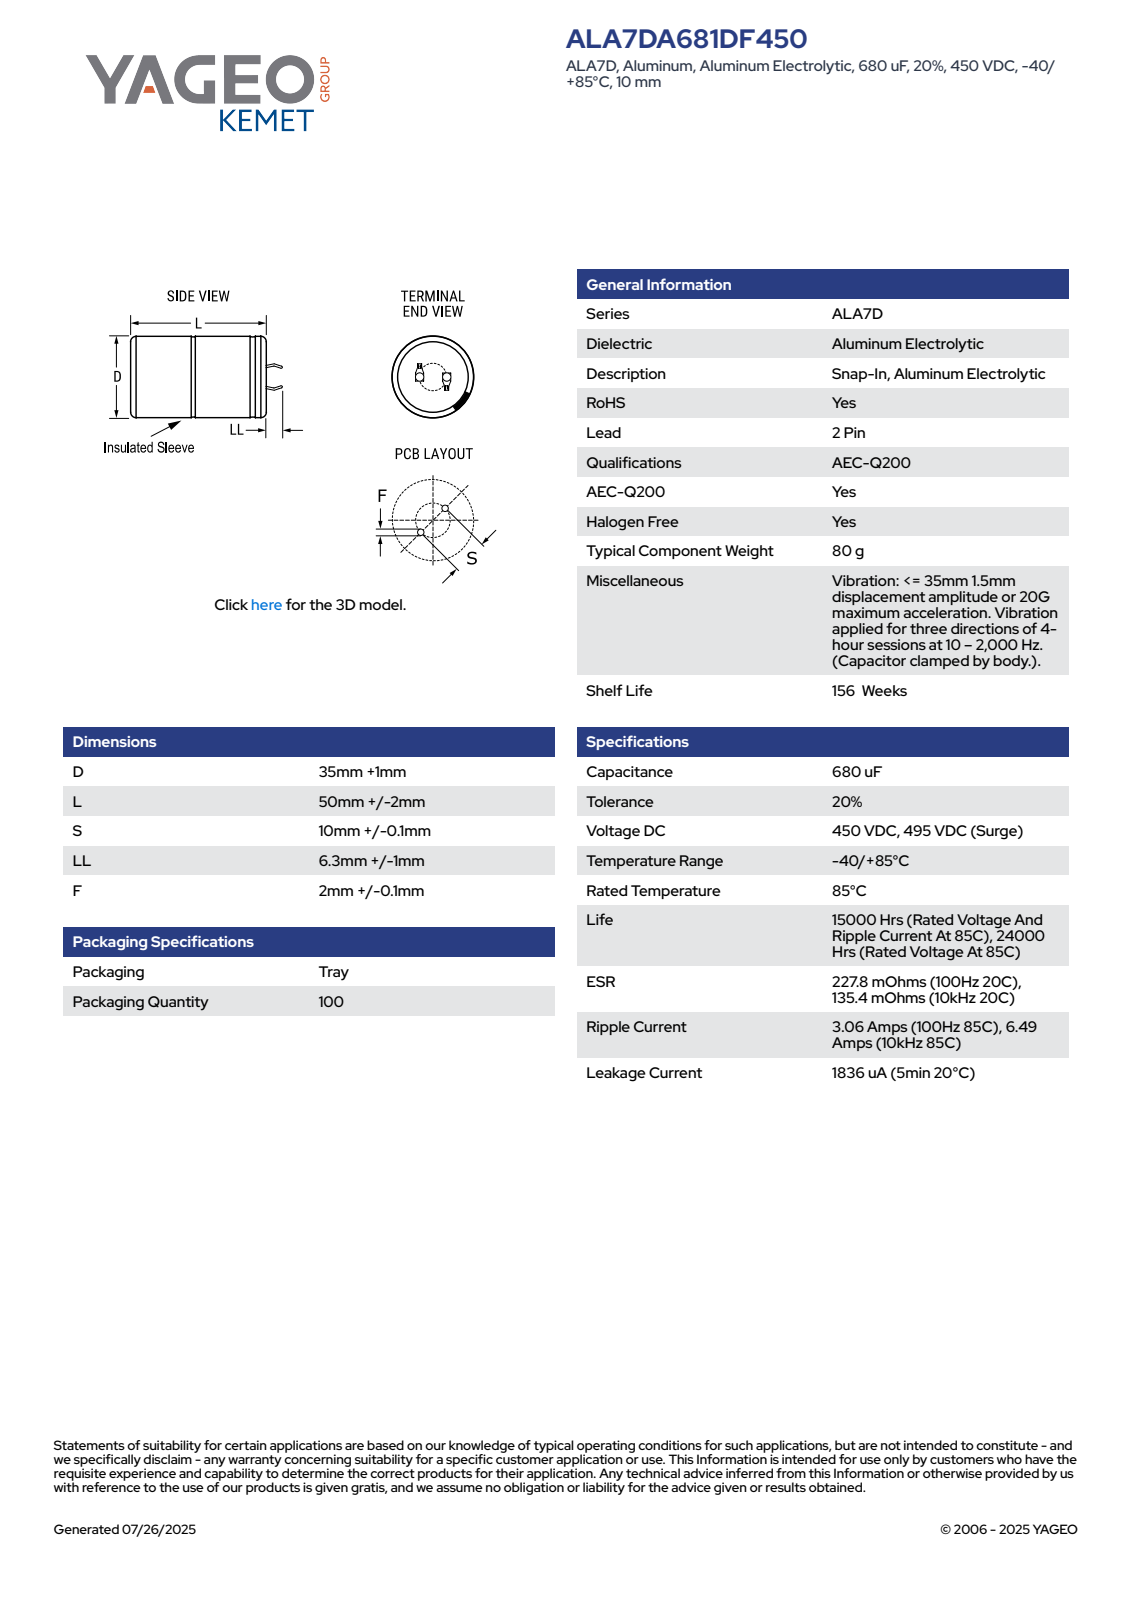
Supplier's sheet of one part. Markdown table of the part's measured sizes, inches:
| quantity | value |
| --- | --- |
| part name | CARS_K2PAV_35X50_D36L52S10LL7.3F2.1 |
| STEP written by | SolidWorks 2021 (AUTOMOTIVE_DESIGN) |
| units | inches |
| bodies | 1 solid, 106 faces (52 planar, 11 cylindrical, 43 other) |
| overall size | 2.334 × 1.417 × 1.417 |
| volume | 3.195 in³ |
| surface area | 12.36 in² |
| round holes (diameter × count) | 1.254 × 1 |
| round bosses / shafts (diameter × count) | 1.417 × 1 |
| partial cylindrical surfaces (radius × count) | 0.708 × 1 |
| main face-to-face distances | 2.047, 0.024, 2.067, 0.02, 0.279, 0.301, 0.053, 0.03, 0.302, 0.255 |
